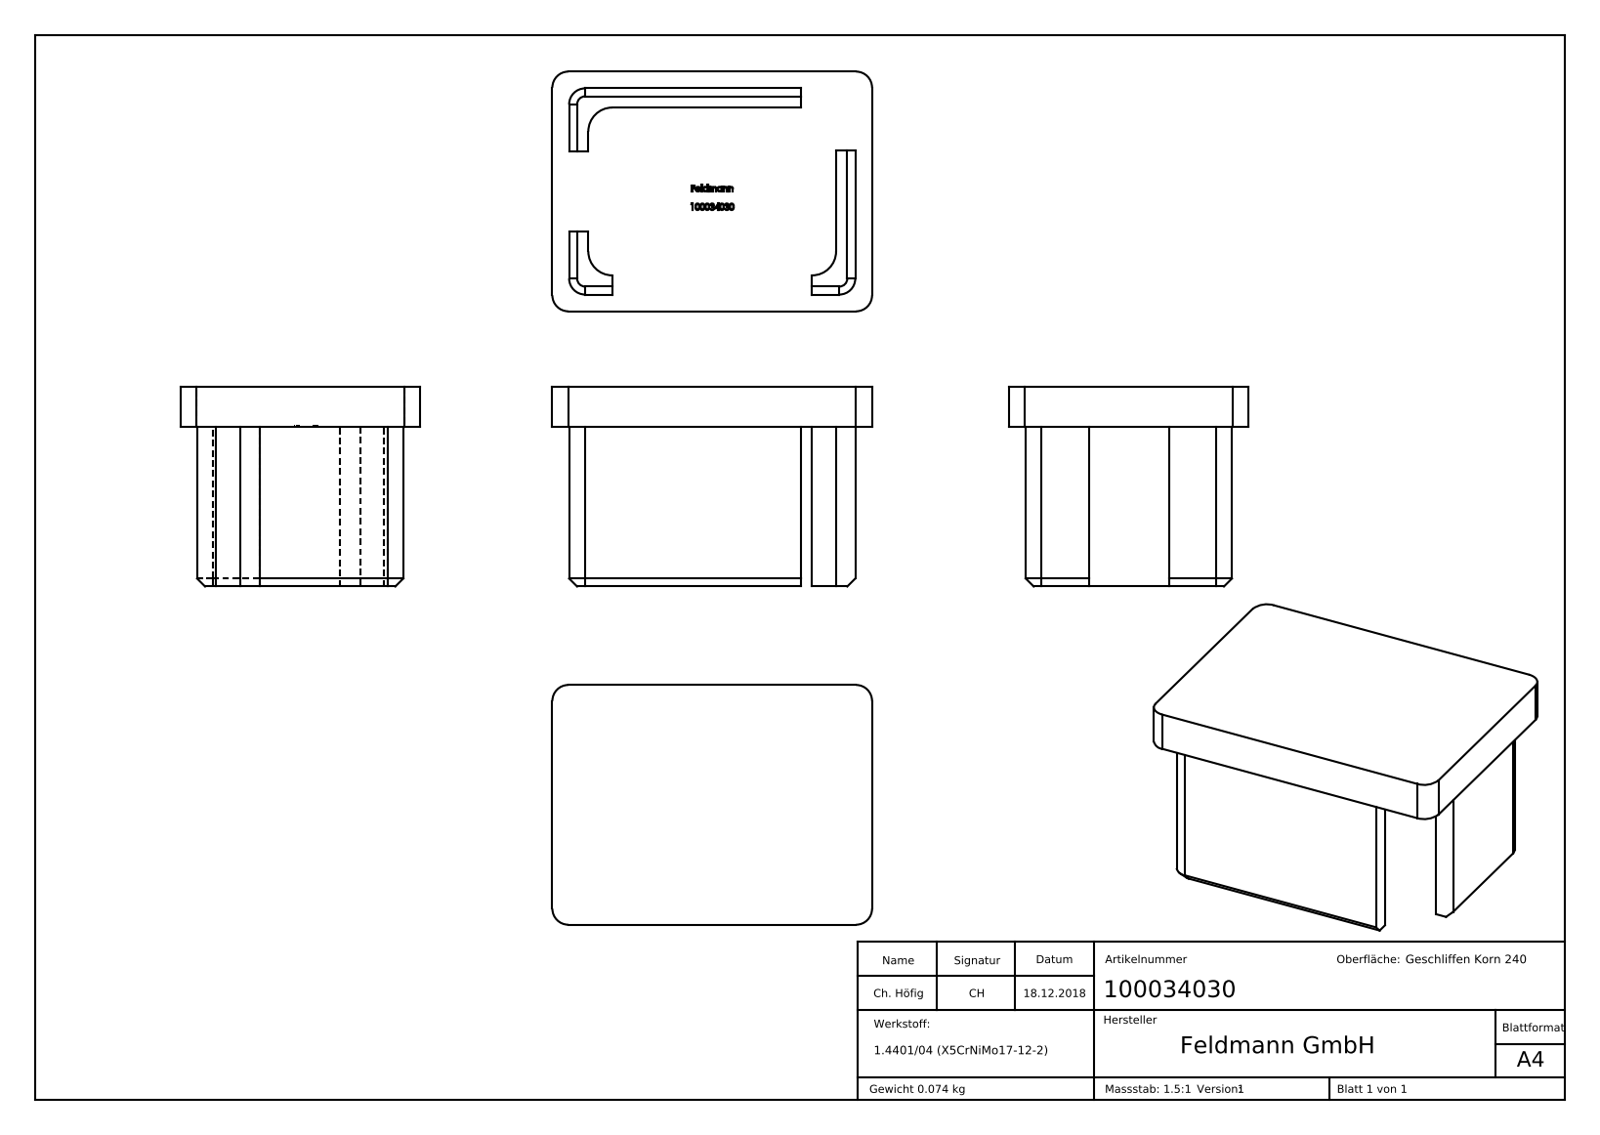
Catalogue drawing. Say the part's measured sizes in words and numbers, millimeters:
The part is named "100034030". Its 3-D file was written by "SolidWorks 2015 (CONFIG_CONTROL_DESIGN)". It is 1 solid with 270 faces: 136 planar, 10 cylindrical and 124 other. Overall it measures 40 by 30 by 25 millimeters. Its volume is 9 199 cubic millimeters and its surface area 5 852 square millimeters. Partial cylindrical surfaces (rounded edges, fillets, slot ends): 7 of radius 2, 3 of radius 3. The main face-to-face distances are 5, 2.4, 2.1, 4.5, 33.4, 27.9, 37.9, 35.5, 35.8, 20.
